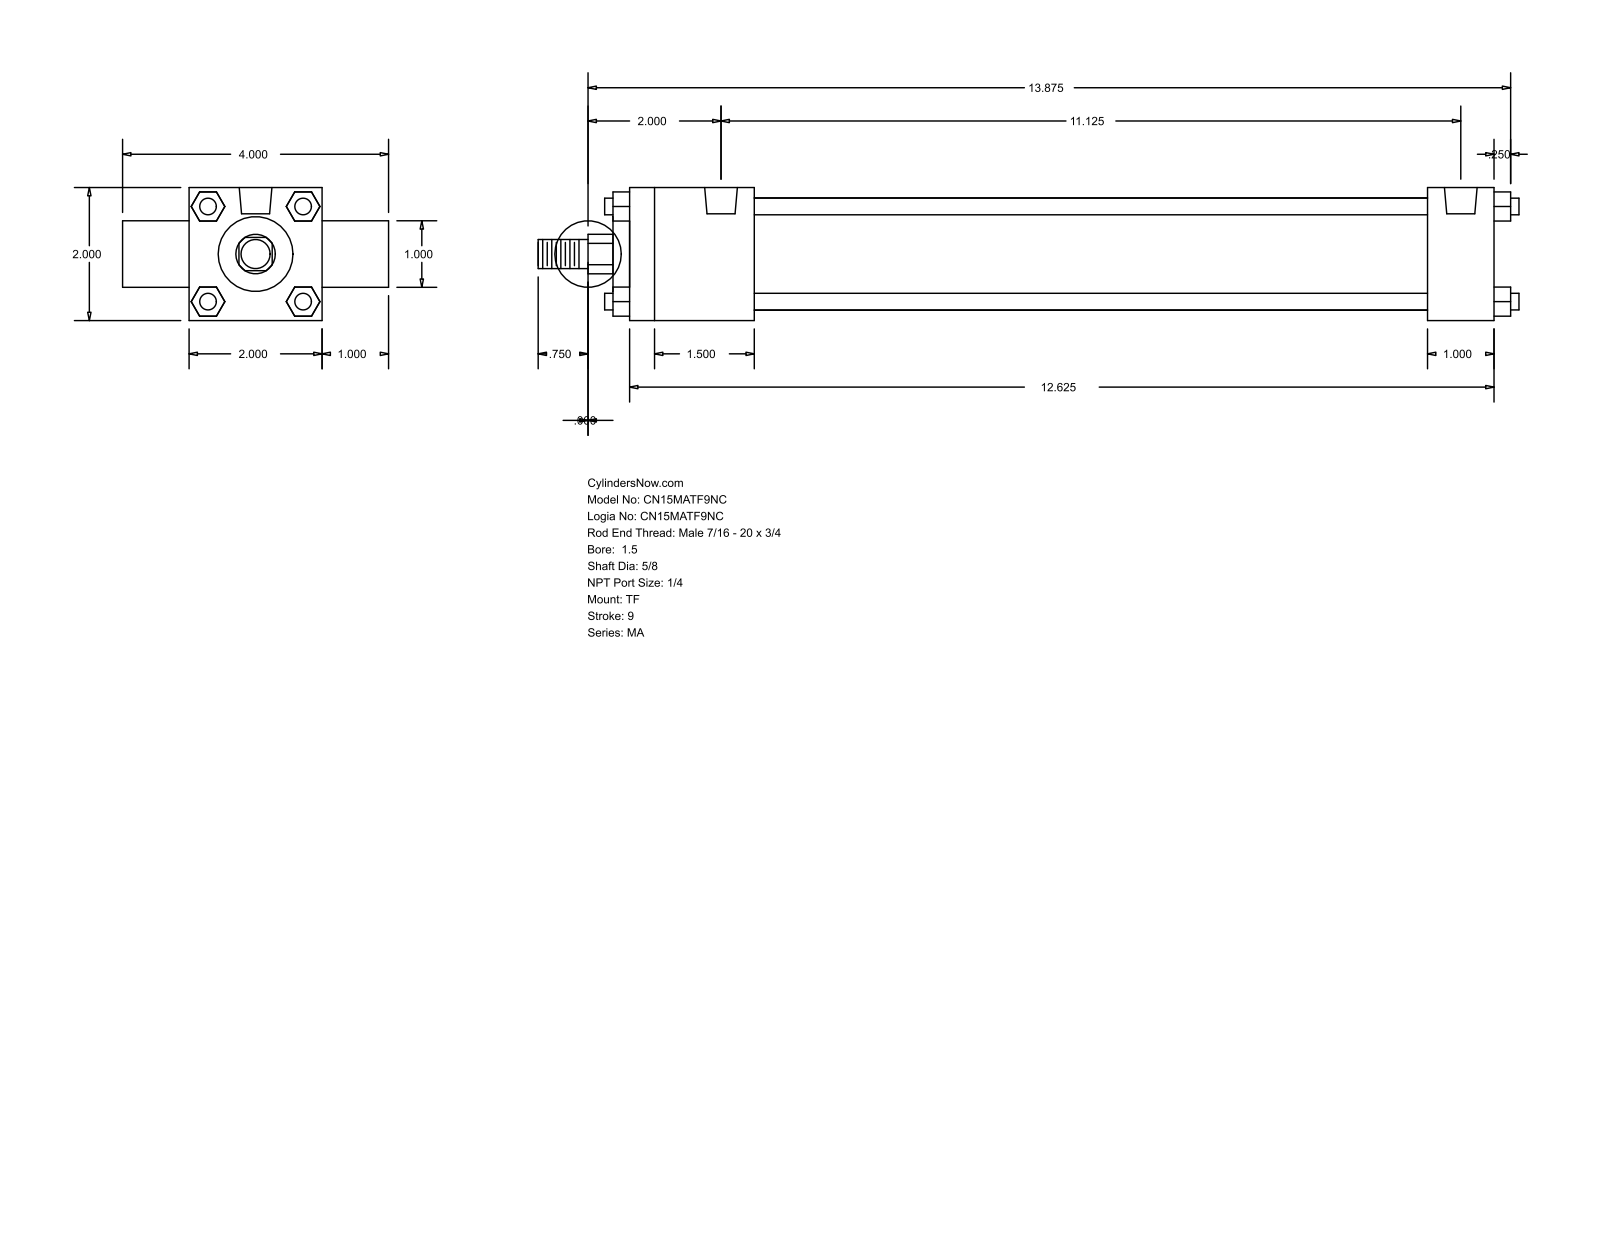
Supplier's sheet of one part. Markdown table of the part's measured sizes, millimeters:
| quantity | value |
| --- | --- |
| part name | MA_TF__0150_0.625 |
| STEP written by | GSSL Pune (CONFIG_CONTROL_DESIGN) |
| units | millimeters |
| bodies | 0 solids, 120 faces (92 planar, 28 cylindrical, 0 other) |
| overall size | 374.65 × 101.6 × 50.8 |
| round holes (diameter × count) | 7.94 × 3, 12.49 × 2 |
| round bosses / shafts (diameter × count) | 6.35 × 4, 42.93 × 1, 28.57 × 1, 25.4 × 1, 15.88 × 1, 11.11 × 1 |
| partial cylindrical surfaces (radius × count) | 7.54 × 1 |
| main face-to-face distances | 50.8, 330.19, 25.4, 76.2, 47.62, 304.8, 257.18, 282.57, 25.39, 6.35 |
| hole center spacings | 282.58 |
